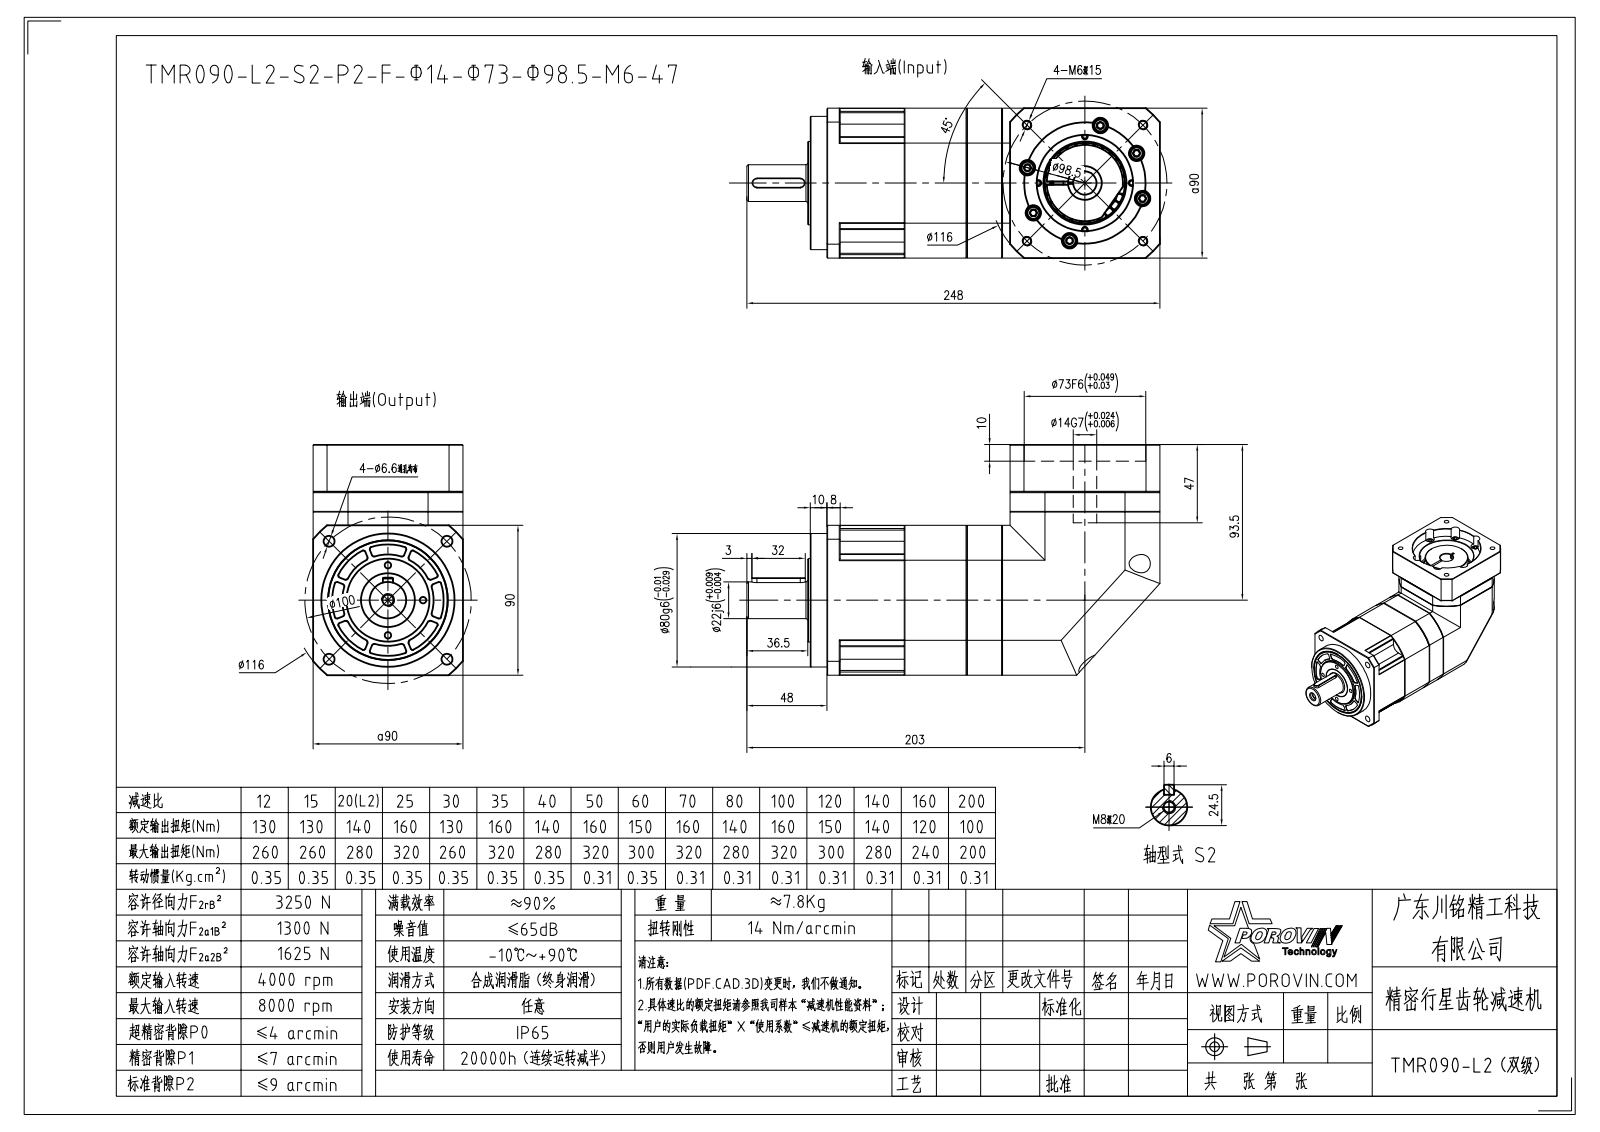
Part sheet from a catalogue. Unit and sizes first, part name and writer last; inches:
Units: inches
Overall size (bounding box): 9.764 × 5.453 × 3.543
Round holes (diameter × count): ⌀0.213 ×12, ⌀0.217 ×12, ⌀0.374 ×12, ⌀0.26 ×10, ⌀0.165 ×7, ⌀0.197 ×5, ⌀0.256 ×5, ⌀0.157 ×4, ⌀0.263 ×4, ⌀0.433 ×4, ⌀0.268 ×1, ⌀0.331 ×1
Round bosses / shafts (diameter × count): ⌀0.335 ×12, ⌀0.315 ×12, ⌀0.197 ×12, ⌀0.394 ×4, ⌀0.389 ×4, ⌀0.236 ×4, ⌀3.15 ×1, ⌀3.071 ×1
Partial cylindrical surfaces — rounded edges, fillets, slot ends (radius × count): R0.039 ×92, R0.295 ×4, R2.008 ×3, R0.118 ×2, R2.283 ×2, R0.157 ×1, R0.207 ×1, R0.817 ×1
Main face-to-face distances: 3.543, 0.472, 0.846, 0.839, 1.476, 2.315, 2.323, 4.331, 0.394, 3.858
Hole centre spacings: 1.407, 1.077, 1.502, 1.732, 2.601, 2.619, 2.675, 0.537
Volume: 98.25 in³ · Surface area: 372.7 in²
Bodies: 44 solids, 1333 faces (530 planar, 564 cylindrical, 239 other)
Part name (STEP PRODUCT): M900001; HEXAGON_SOCKET_HEAD_CAP_SC-9564; SPRING_LOCK_WASHERS--NORM-19349; HEXAGON_SOCKET_HEAD_CAP_S-19443 (+8 more)
STEP written by: CREO PARAMETRIC BY PTC INC, 2020053 (CONFIG_CONTROL_DESIGN)
